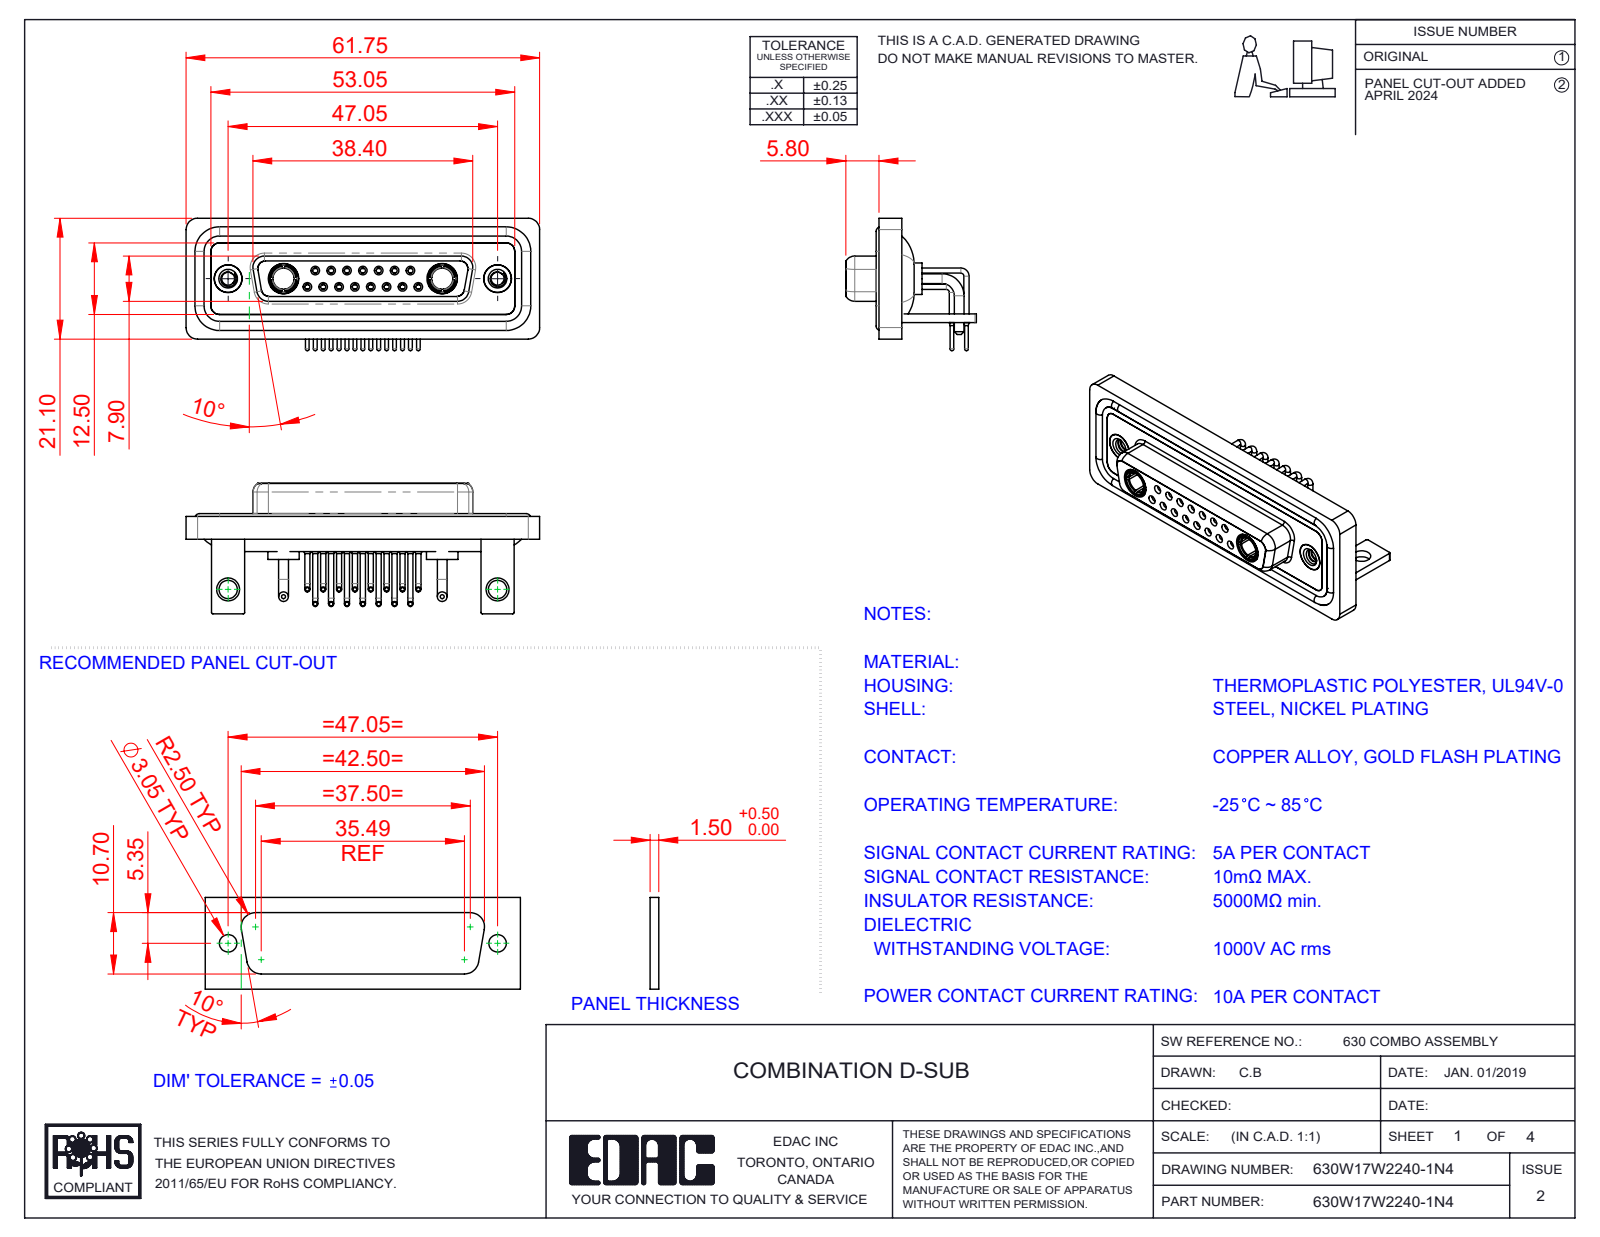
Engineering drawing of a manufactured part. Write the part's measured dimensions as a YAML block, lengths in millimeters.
part_name: "630Combo Waterproof Housing_25 Contacts; 630Combo Housing_17W2; 630W17W2240-1N4; 630Combo Shell Rear_25 Contacts (+6 more)"
step_written_by: "SolidWorks 2023 (CONFIG_CONTROL_DESIGN)"
units: millimeters
bodies: {solids: 28, faces: 1385, planar: 408, cylindrical: 607, other: 370}
overall_size: [61.75, 23.12, 22.8]
volume: 8738
surface_area: 15164
round_holes:
  - {diameter: 0.9, count: 15}
  - {diameter: 1.1, count: 15}
  - {diameter: 1.5, count: 15}
  - {diameter: 2, count: 15}
  - {diameter: 1.6, count: 8}
  - {diameter: 1.7, count: 7}
  - {diameter: 4.85, count: 4}
  - {diameter: 2.26, count: 2}
  - {diameter: 3.2, count: 2}
  - {diameter: 3.7, count: 2}
  - {diameter: 4, count: 2}
  - {diameter: 4.05, count: 2}
round_bosses_or_shafts:
  - {diameter: 0.9, count: 15}
  - {diameter: 0.65, count: 15}
  - {diameter: 1.6, count: 11}
  - {diameter: 1.7, count: 4}
  - {diameter: 5.5, count: 2}
  - {diameter: 5.2, count: 2}
  - {diameter: 4.96, count: 2}
  - {diameter: 4.95, count: 2}
partial_cylinders:
  - {radius: 2, count: 19}
  - {radius: 1.5, count: 18}
  - {radius: 0.25, count: 16}
  - {radius: 1.35, count: 8}
  - {radius: 1.6, count: 8}
  - {radius: 0.5, count: 5}
  - {radius: 0.6, count: 4}
  - {radius: 0.65, count: 4}
face_to_face_distances: [0.4, 1.8, 2.9, 3.7, 1.5, 4.1, 1.1, 1.4, 1.6, 3.1]
hole_center_spacings: [3.16, 2.77, 5.54, 8.31, 5.04, 7.49, 11.08, 5.03]
